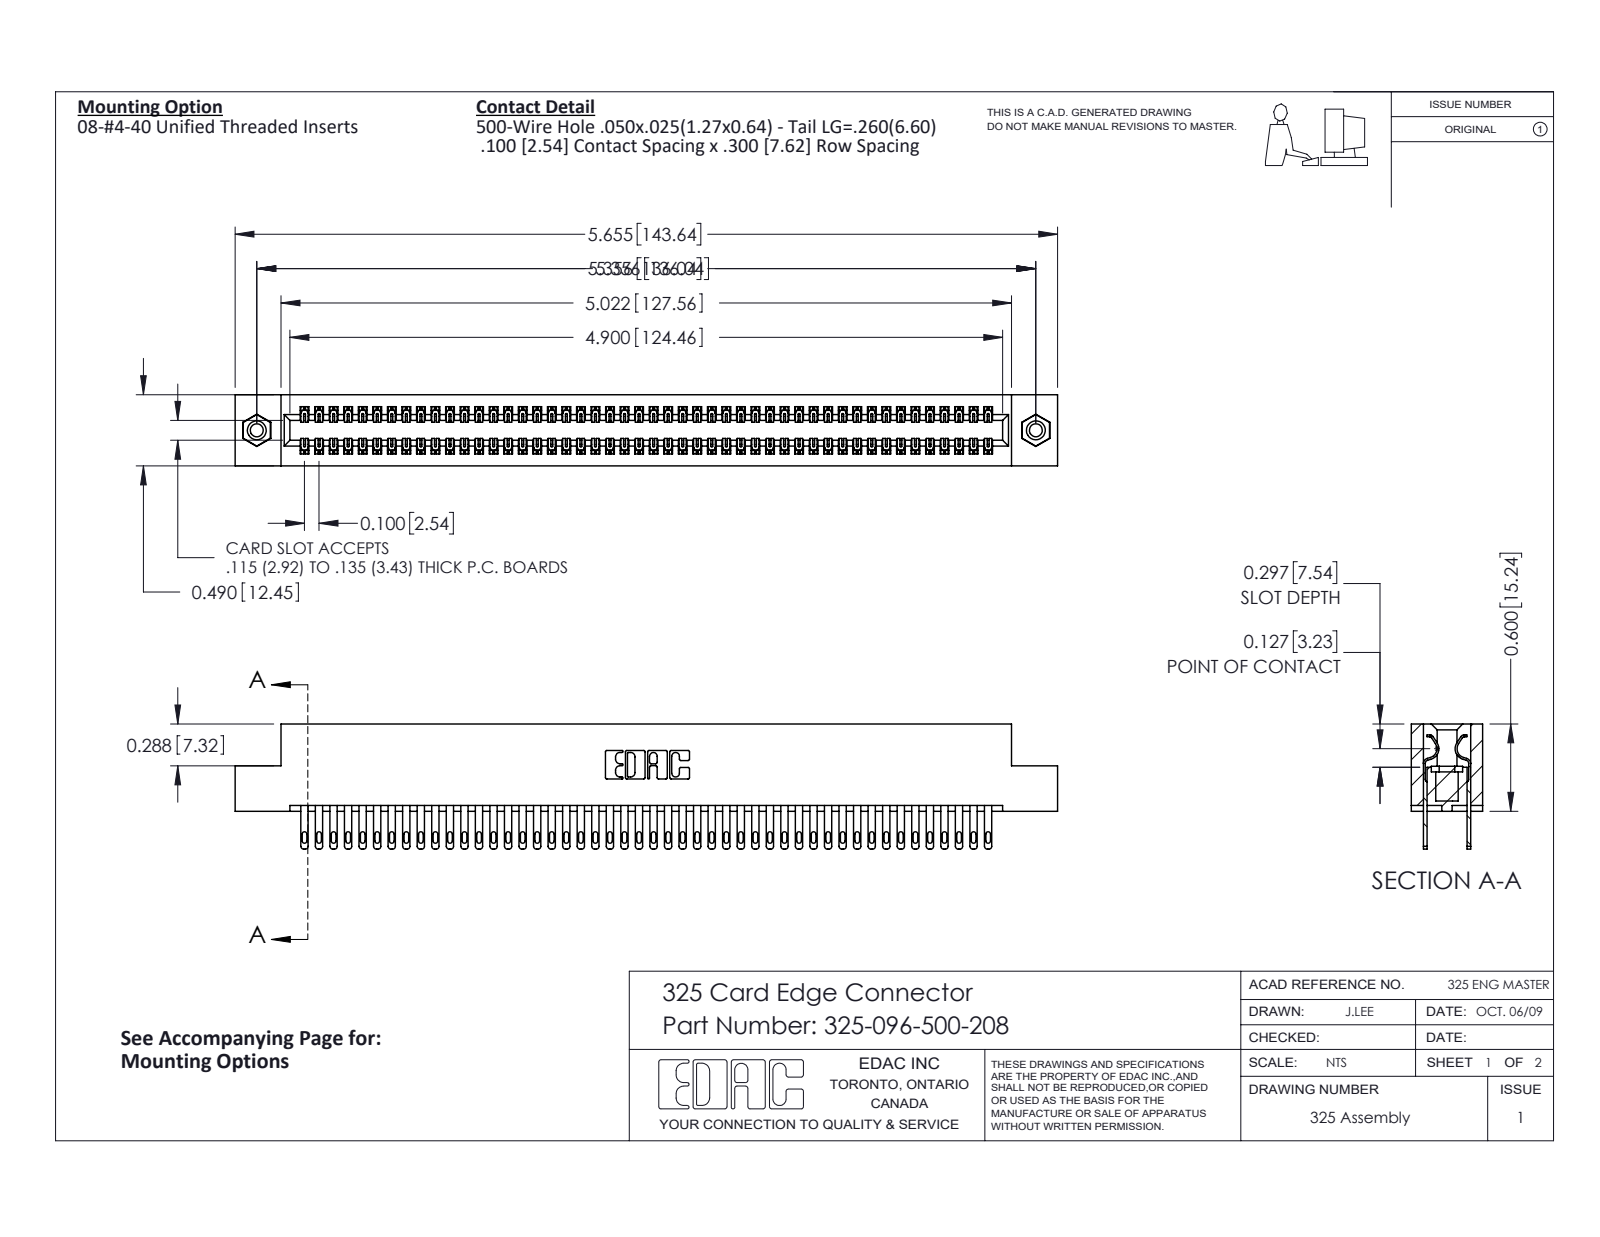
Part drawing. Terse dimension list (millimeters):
name: 345-250-001_345-250-003-102; 325-292-001_325-293-100; 325 Part_TI; 325-096-500-208
written by: SolidWorks 2016 (CONFIG_CONTROL_DESIGN)
unit: mm
bodies: 99 solids, 4782 faces (2982 planar, 1784 cylindrical, 16 other)
size: 143.6 × 21.8 × 12.4
volume: 18 880 mm³; area: 24 010 mm²
holes: 2× ⌀2.3, 2× ⌀3.2, 2× ⌀4.1
bosses: 2× ⌀3.9
rounds: 144× R0.2, 96× R0.4, 96× R0.5, 22× R0.3, 6× R0.2, 6× R0.8, 3× R0.7, 2× R0.4
face distances: 2.1, 10.3, 7.6, 2.7, 9.7, 0.6, 12.4, 8.3, 7, 14.2
hole spacings: 136
